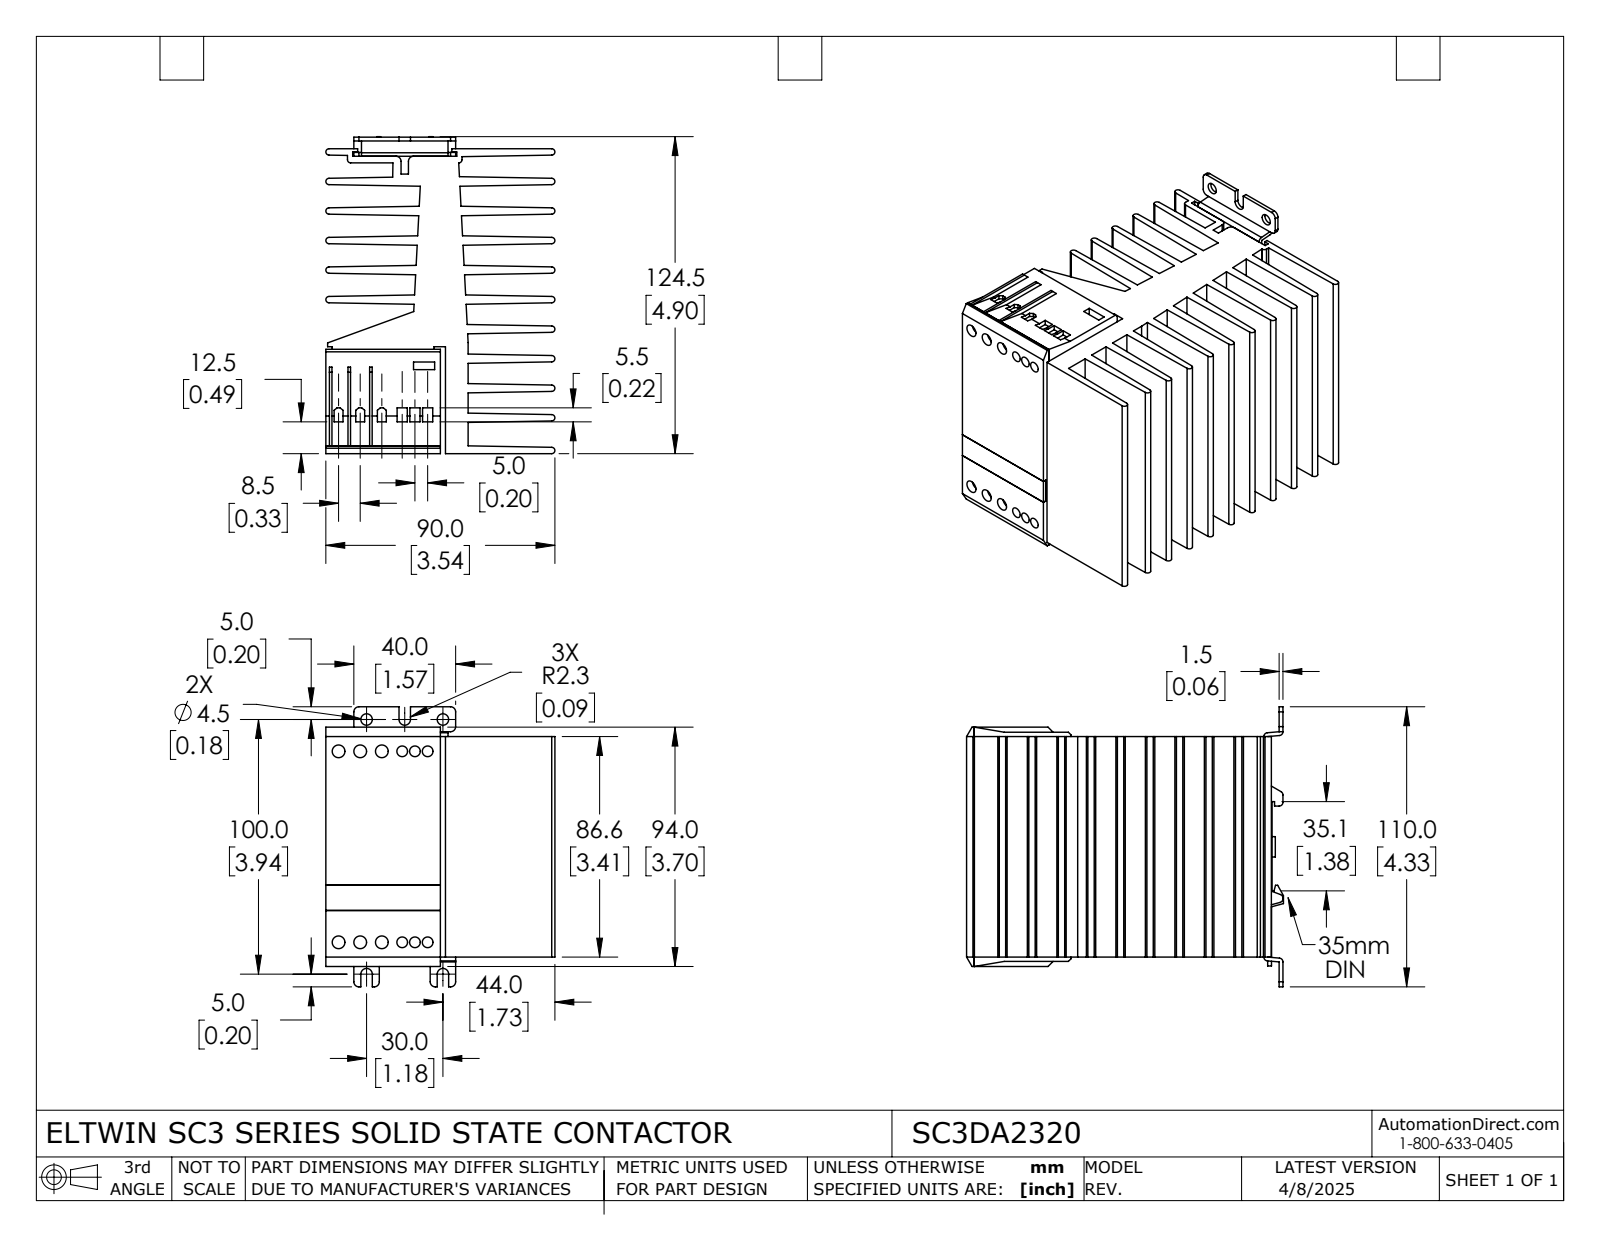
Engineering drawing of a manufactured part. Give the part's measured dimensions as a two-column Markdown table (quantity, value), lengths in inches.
| quantity | value |
| --- | --- |
| part name | SC3DA2320 |
| STEP written by | SolidWorks 2021 (AUTOMOTIVE_DESIGN) |
| units | inches |
| bodies | 5 solids, 440 faces (326 planar, 114 cylindrical, 0 other) |
| overall size | 4.902 × 4.331 × 3.543 |
| volume | 31.2 in³ |
| surface area | 277.9 in² |
| round holes (diameter × count) | 0.165 × 6, 0.173 × 6, 0.197 × 6, 0.236 × 6, 0.177 × 2 |
| round bosses / shafts (diameter × count) | 0.315 × 1 |
| partial cylindrical surfaces (radius × count) | 0.049 × 19, 0.079 × 18, 0.059 × 10, 0.051 × 4, 0.089 × 3 |
| main face-to-face distances | 0.457, 0.913, 1.37, 0.159, 0.3, 0.157, 1.827, 1.669, 1.828, 2.126 |
| hole center spacings | 2.953, 0.197, 0.335, 2.959, 2.972, 1.181, 0.315, 0.394 |
